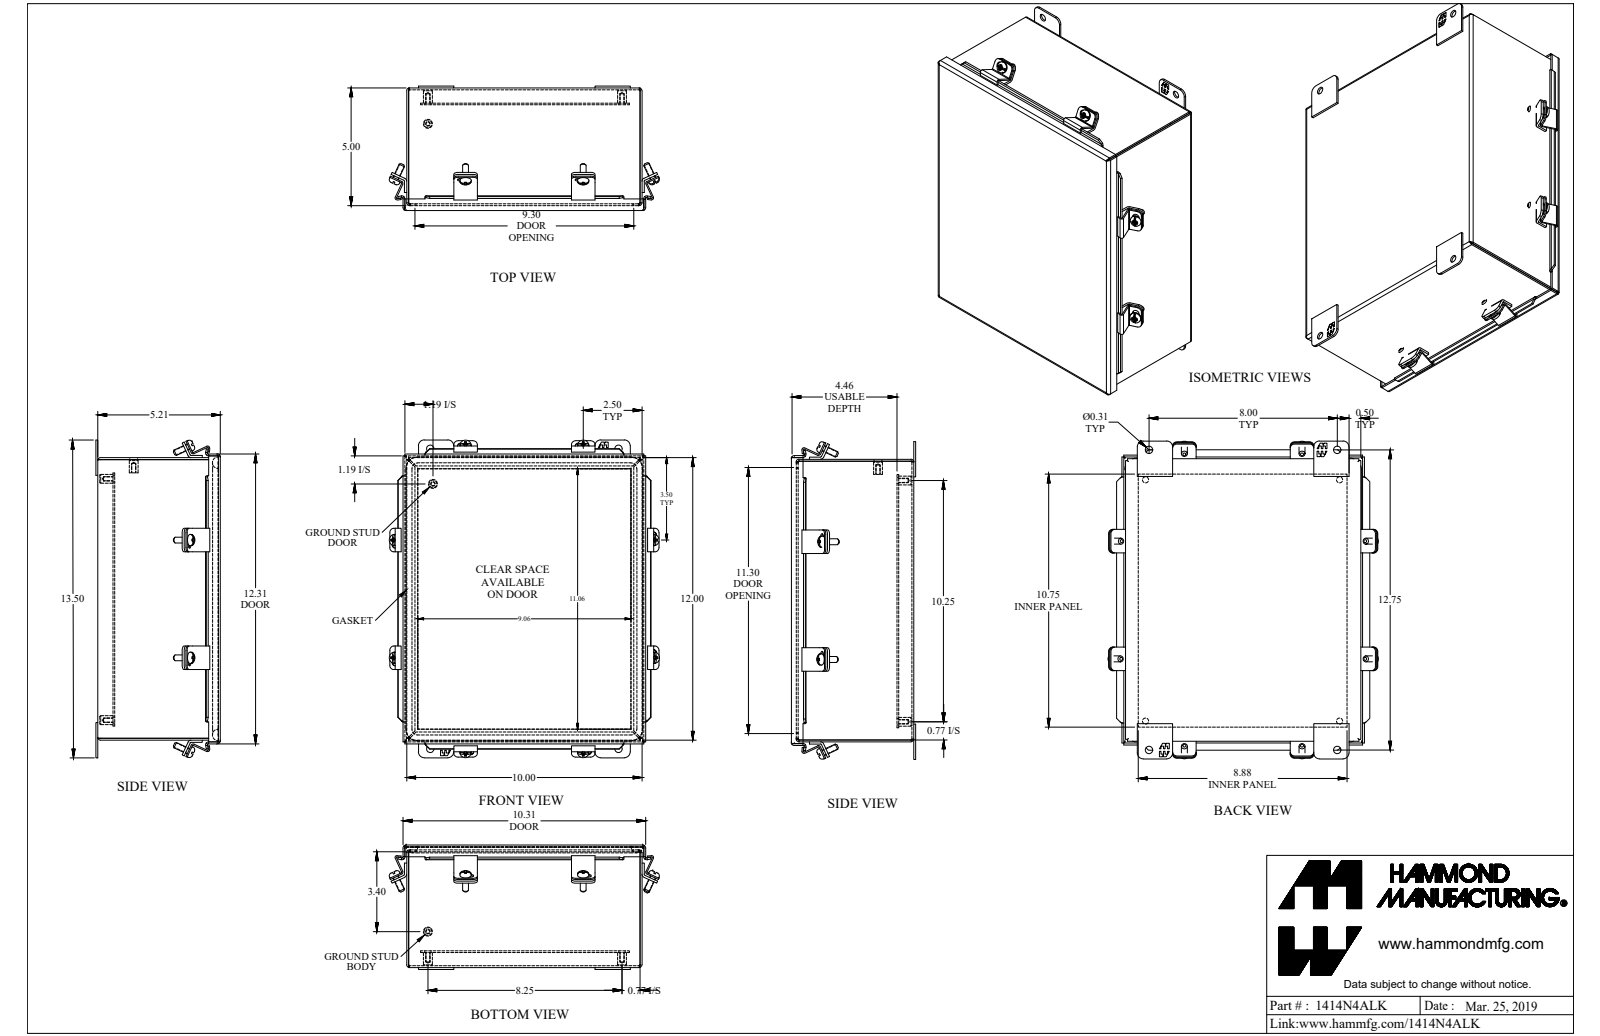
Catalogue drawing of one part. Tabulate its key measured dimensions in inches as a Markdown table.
| quantity | value |
| --- | --- |
| part name | 1414N4ALK |
| STEP written by | SolidWorks 2018 (AUTOMOTIVE_DESIGN) |
| units | inches |
| bodies | 38 solids, 1051 faces (719 planar, 238 cylindrical, 94 other) |
| overall size | 13.5 × 11.49 × 5.286 |
| volume | 54.15 in³ |
| surface area | 1 377 in² |
| round holes (diameter × count) | 0.213 × 8, 0.159 × 6, 0.265 × 4, 0.313 × 4 |
| round bosses / shafts (diameter × count) | 0.48 × 8, 0.25 × 8, 0.375 × 6, 0.33 × 6 |
| partial cylindrical surfaces (radius × count) | 0.141 × 16, 0.188 × 16, 0.25 × 12, 0.01 × 10, 0.029 × 8, 0.036 × 8, 0.048 × 8, 0.086 × 8 |
| main face-to-face distances | 0.081, 5.125, 5.206, 5.044, 9.919, 0.562, 0.643, 4.563, 4.482, 11.919 |
| hole center spacings | 5, 8, 8.25, 10.25, 12.75, 13.158, 15.052, 0.31 |
